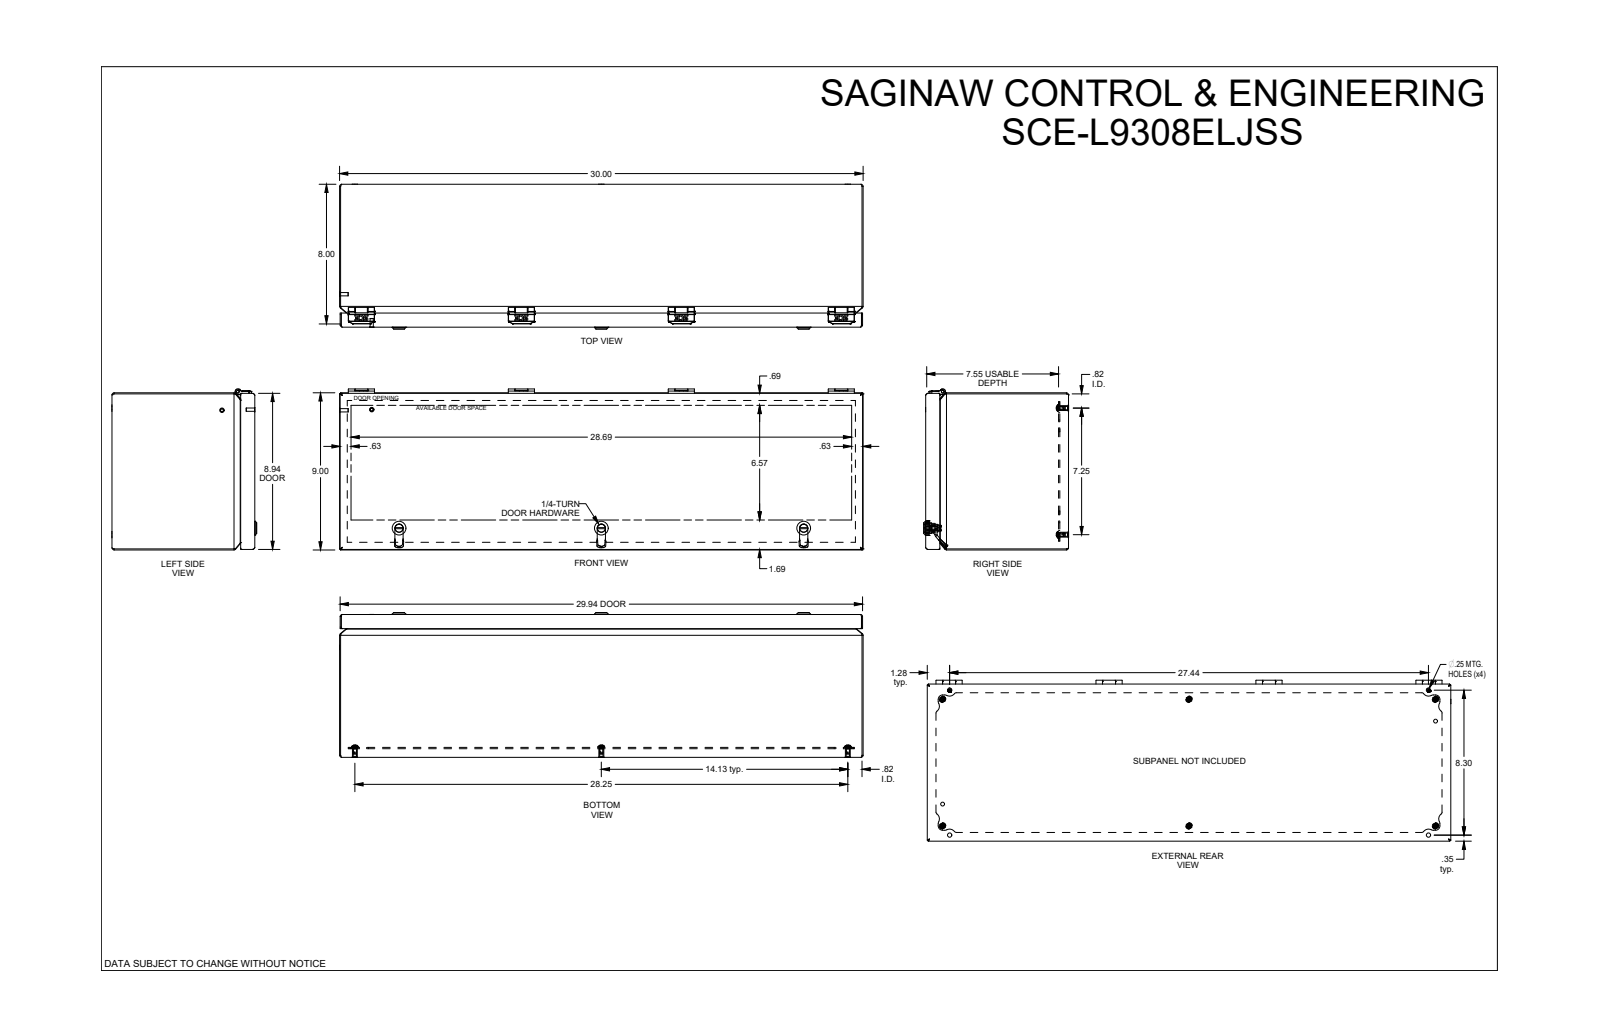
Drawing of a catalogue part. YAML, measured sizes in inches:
part_name: "SCE-L9308ELJSS"
step_written_by: "SolidWorks 2022 (AUTOMOTIVE_DESIGN)"
units: inches
bodies: {solids: 56, faces: 1766, planar: 698, cylindrical: 590, other: 478}
overall_size: [30.004, 9.22, 8.296]
volume: 96.6
surface_area: 3046
round_holes:
  - {diameter: 0.19, count: 6}
  - {diameter: 0.25, count: 6}
  - {diameter: 0.284, count: 6}
  - {diameter: 0.02, count: 4}
  - {diameter: 0.1, count: 4}
  - {diameter: 0.266, count: 4}
  - {diameter: 0.2, count: 3}
  - {diameter: 0.239, count: 3}
  - {diameter: 0.254, count: 3}
  - {diameter: 0.269, count: 3}
  - {diameter: 0.282, count: 3}
  - {diameter: 0.326, count: 3}
round_bosses_or_shafts:
  - {diameter: 0.188, count: 8}
  - {diameter: 0.16, count: 8}
  - {diameter: 0.373, count: 6}
  - {diameter: 0.28, count: 6}
  - {diameter: 0.26, count: 4}
  - {diameter: 0.237, count: 4}
  - {diameter: 0.23, count: 4}
  - {diameter: 0.18, count: 4}
partial_cylinders:
  - {radius: 0.03, count: 52}
  - {radius: 0.013, count: 41}
  - {radius: 0.01, count: 26}
  - {radius: 0.02, count: 17}
  - {radius: 0.05, count: 16}
  - {radius: 0.25, count: 13}
  - {radius: 0.125, count: 11}
  - {radius: 0.06, count: 10}
face_to_face_distances: [0.059, 8.941, 0.06, 8.125, 8.066, 8.185, 8.126, 7.554, 0.437, 0.571]
hole_center_spacings: [9.167, 14.125, 14.125, 28.25, 15.877, 7.25, 7.251, 15.71]
